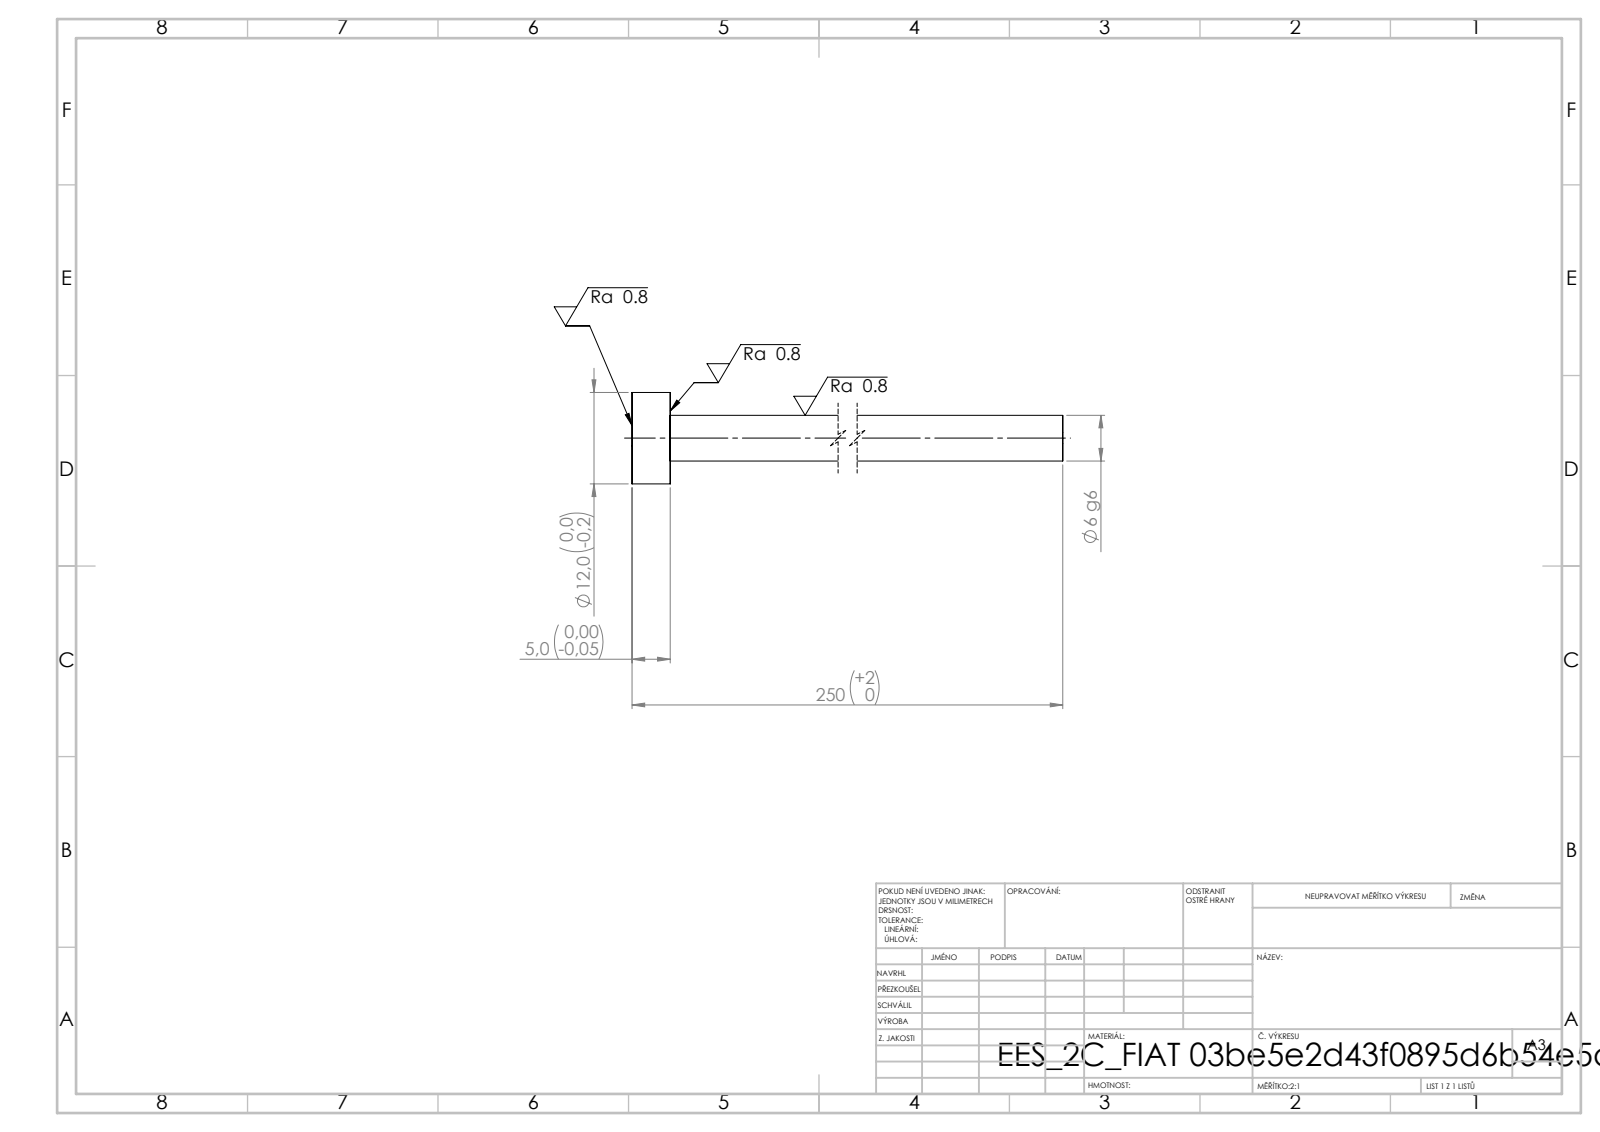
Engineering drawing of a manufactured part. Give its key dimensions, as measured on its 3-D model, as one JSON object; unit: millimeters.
{"step_written_by": "SolidWorks 2019 (CONFIG_CONTROL_DESIGN)", "units": "millimeters", "bodies": {"solids": 1, "faces": 7, "planar": 3, "cylindrical": 4, "other": 0}, "overall_size": [250, 12, 12], "volume_mm3": 7493, "surface_area_mm2": 5033, "round_bosses_or_shafts": [[12, 1], [6, 1]], "face_to_face_distances": [5, 250, 245]}
